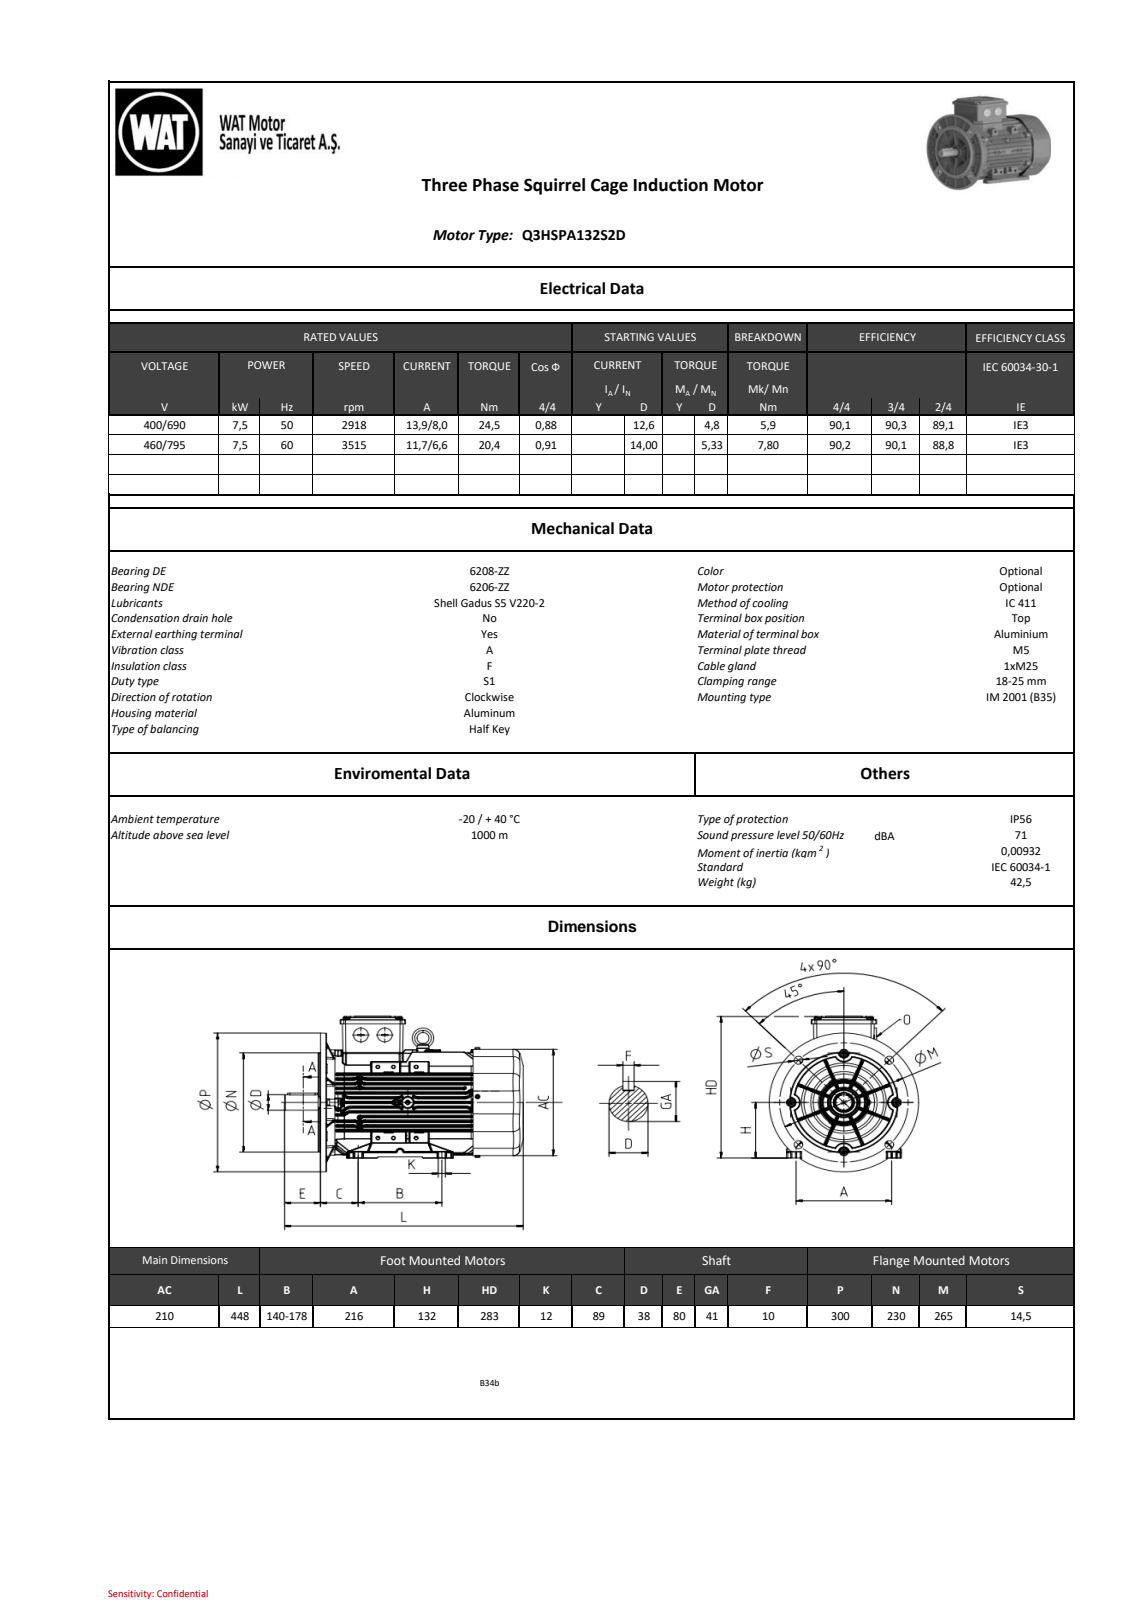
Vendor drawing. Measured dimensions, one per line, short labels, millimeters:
name: Ar311510F80554pv
written by: SIEMENS PLM Software NX 9.0 (AUTOMOTIVE_DESIGN)
unit: mm
bodies: 1 solid, 12970 faces (2715 planar, 3822 cylindrical, 6433 other)
size: 447.4 × 301.09 × 300.25
holes: 4× ⌀6.65, 4× ⌀8.3, 3× ⌀3.5, 3× ⌀4.92, 2× ⌀5, 2× ⌀12, 2× ⌀27.8, 1× ⌀3.3, 1× ⌀4, 1× ⌀4.72, 1× ⌀6.5, 1× ⌀8
bosses: 12× ⌀8, 12× ⌀2, 5× ⌀4, 4× ⌀14.8, 4× ⌀13, 4× ⌀10, 4× ⌀6, 1× ⌀230
rounds: 938× R0.5, 737× R1, 528× R0.8, 255× R2, 52× R3, 28× R0.38, 23× R0.3, 12× R5
face distances: 243, 21.2, 264.2, 5, 1, 21.5, 35.96, 10.99, 99.54, 24.97
hole spacings: 40, 110, 60.38, 62.23, 63.06, 72.62, 123.63, 127.74
